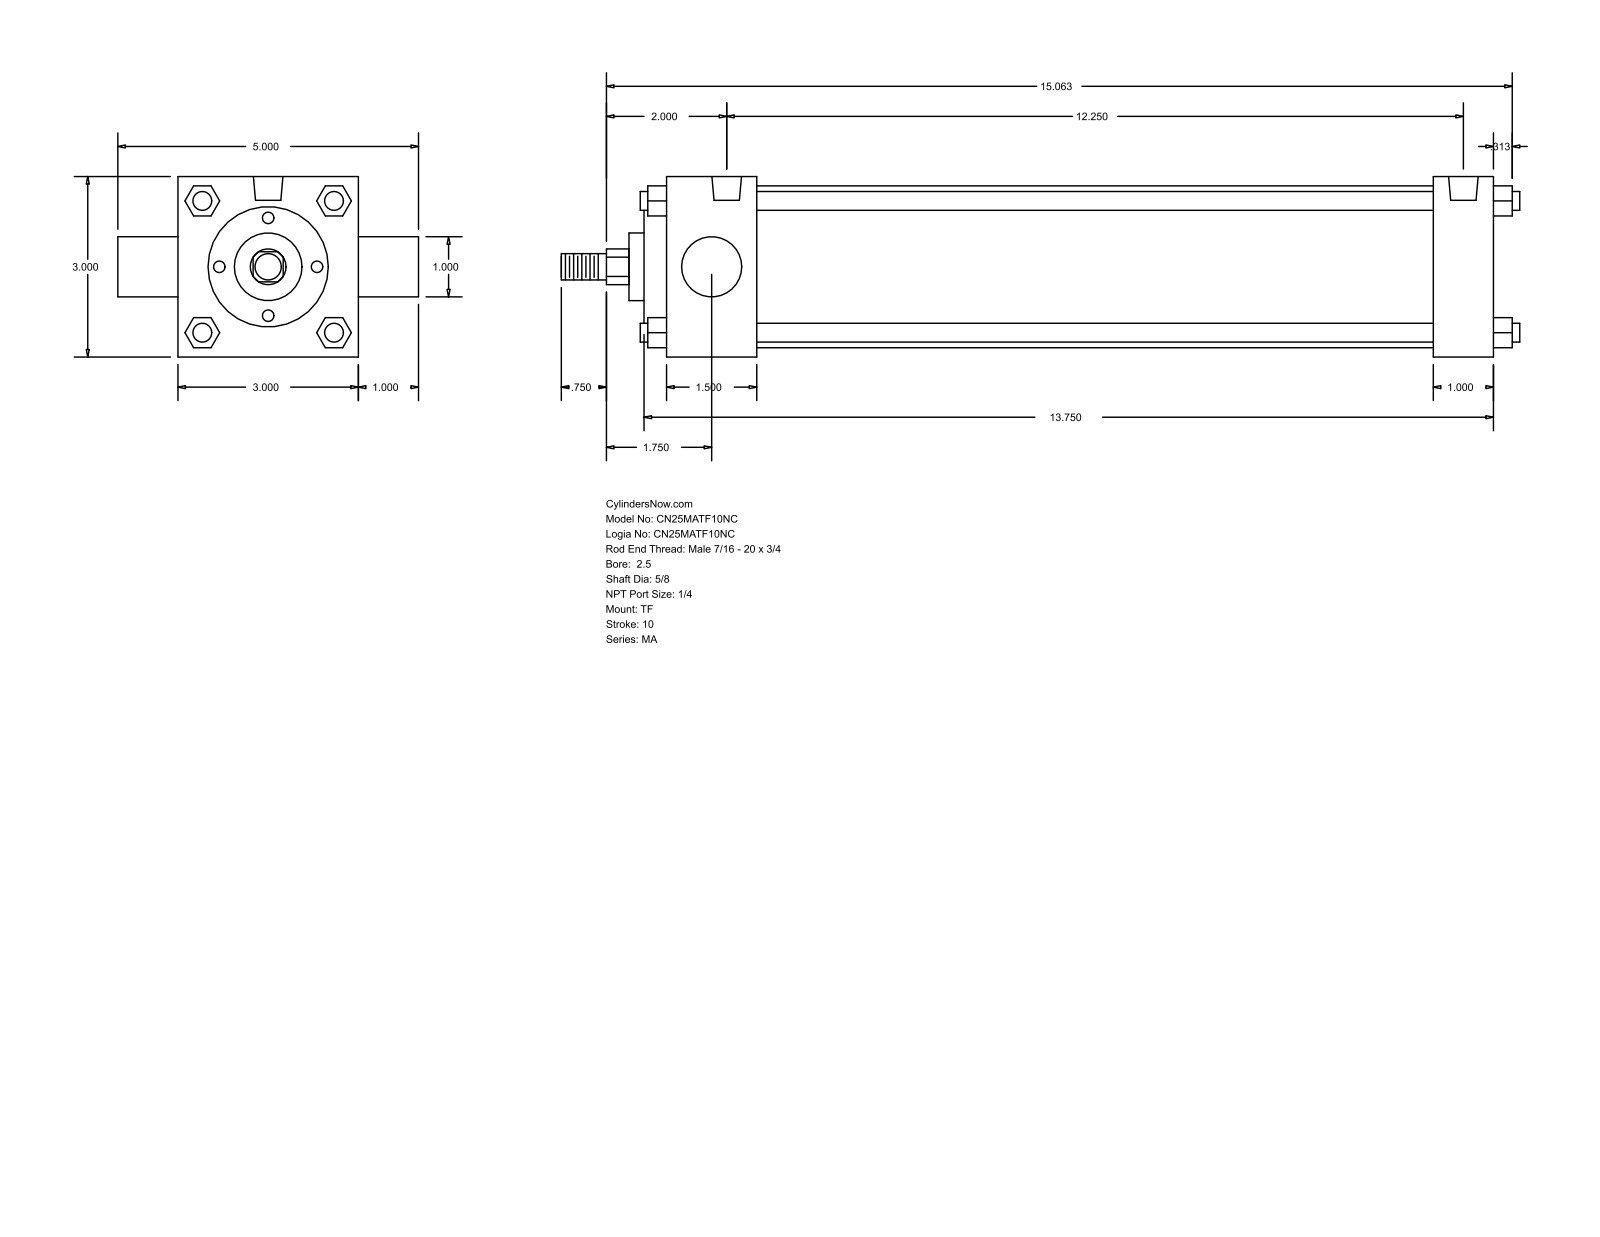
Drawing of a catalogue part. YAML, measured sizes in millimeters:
part_name: "MA_TF__0250_0.625"
step_written_by: "GSSL Pune (CONFIG_CONTROL_DESIGN)"
units: millimeters
bodies: {solids: 0, faces: 122, planar: 93, cylindrical: 29, other: 0}
overall_size: [404.81, 127, 76.2]
round_holes:
  - {diameter: 7.94, count: 3}
  - {diameter: 12.49, count: 2}
round_bosses_or_shafts:
  - {diameter: 7.94, count: 4}
  - {diameter: 68.33, count: 1}
  - {diameter: 50.8, count: 1}
  - {diameter: 28.57, count: 1}
  - {diameter: 25.4, count: 1}
  - {diameter: 15.88, count: 1}
  - {diameter: 11.11, count: 1}
partial_cylinders:
  - {radius: 7.54, count: 1}
face_to_face_distances: [76.2, 349.25, 25.4, 38.1, 323.85, 285.75, 311.15, 12.7, 9.52, 47.62]
hole_center_spacings: [311.15]
